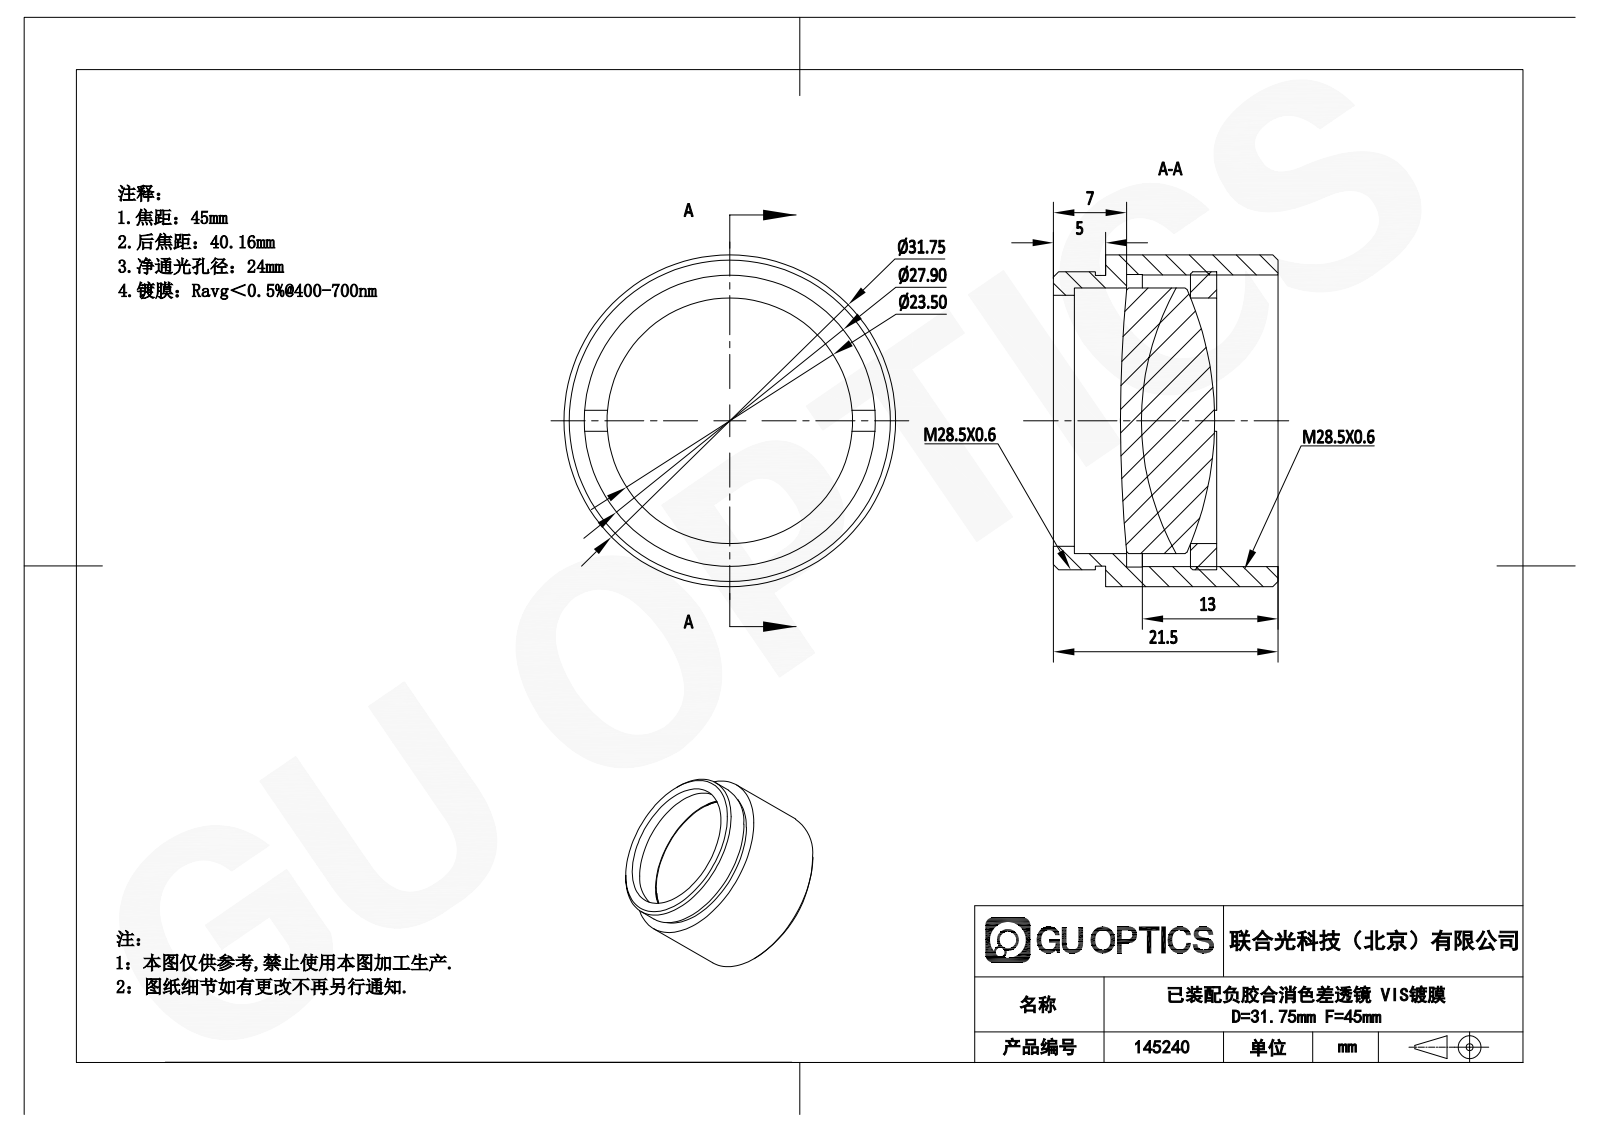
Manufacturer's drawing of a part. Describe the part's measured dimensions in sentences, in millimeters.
The part is named "GL31-025B-045-VIS_Solidworks; M28.5x0.6ѹȦ; APD-ML25-045-VIS". Its 3-D file was written by "SolidWorks 2022 (AUTOMOTIVE_DESIGN)". It is 4 solids with 56 faces: 16 planar, 22 cylindrical and 18 other. Overall it measures 31.76 by 31.76 by 21.5 millimeters. Its volume is 8 129 cubic millimeters and its surface area 7 979 square millimeters. Round holes: 1 of diameter 23.5, 1 of diameter 24, 1 of diameter 27.9, 1 of diameter 28. Round bosses or shafts: 1 of diameter 31.76, 1 of diameter 28.5, 1 of diameter 27.8, 1 of diameter 25.4. The main face-to-face distances are 2, 5, 2.5, 8.12, 10.62, 13.12, 15.62, 21.5, 16.5, 8.38.
